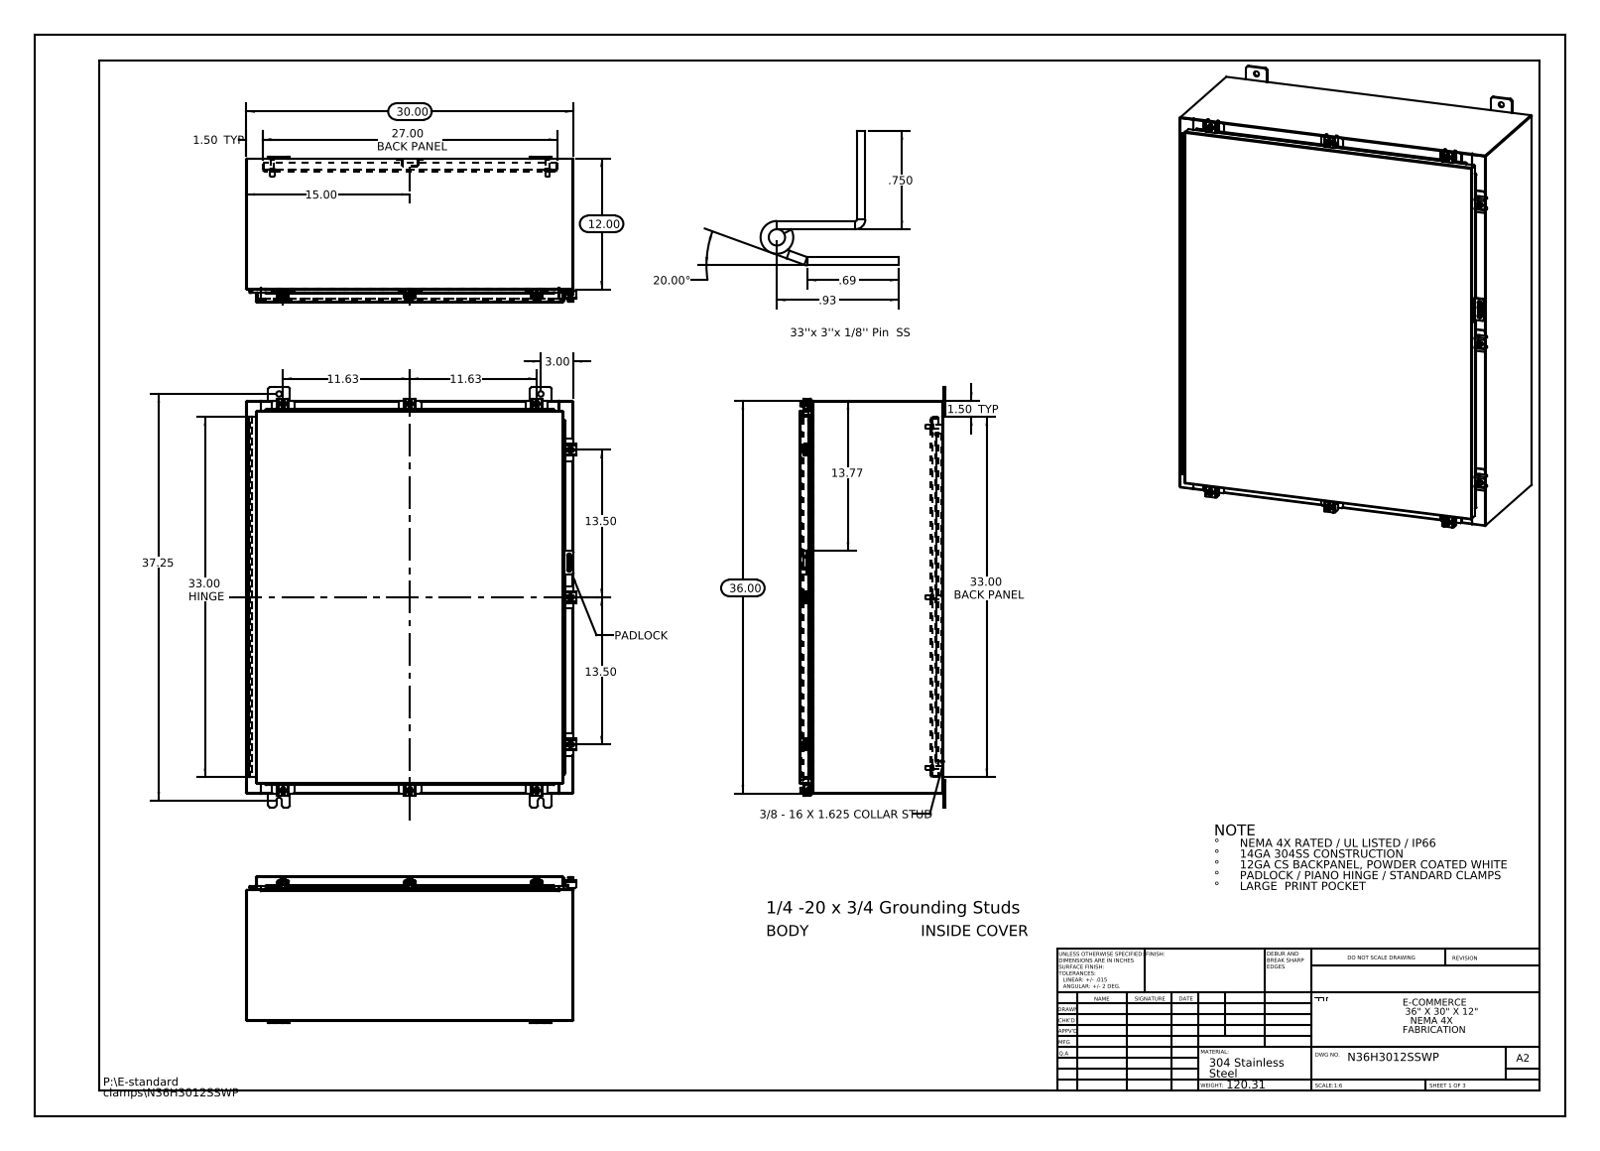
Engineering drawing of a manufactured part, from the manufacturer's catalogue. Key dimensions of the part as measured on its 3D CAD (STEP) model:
Part name (STEP PRODUCT): N36H3012SSWP Hinge Enclosure Side2; N36H3012SSWP Body; N36H3012SSWP; N36H3012SSWP 22104005_DEFAULT (+8 more)
STEP written by: SolidWorks 2013 (CONFIG_CONTROL_DESIGN)
Units: inches
Bodies: 65 solids, 2456 faces (1288 planar, 1028 cylindrical, 140 other)
Overall size (bounding box): 38.5 × 30.211 × 13.389
Volume: 421.7 in³ · Surface area: 10 572 in²
Round holes (diameter × count): ⌀0.5 ×10, ⌀0.213 ×9, ⌀0.26 ×9, ⌀0.125 ×2, ⌀0.125 ×1
Round bosses / shafts (diameter × count): ⌀0.25 ×10, ⌀0.5 ×9, ⌀0.399 ×9, ⌀0.625 ×6, ⌀0.375 ×6, ⌀0.33 ×6
Partial cylindrical surfaces — rounded edges, fillets, slot ends (radius × count): R0.06 ×42, R0.013 ×31, R0.088 ×25, R0.19 ×24, R0.12 ×18, R0.141 ×18, R0.05 ×13, R0.08 ×12
Main face-to-face distances: 0.075, 13.126, 13.051, 13.201, 0.104, 1, 12.126, 1.075, 12.051, 1.179
Hole centre spacings: 15.625, 17.754, 29.694, 33.366, 37.309, 25.25, 35.451, 1.858
